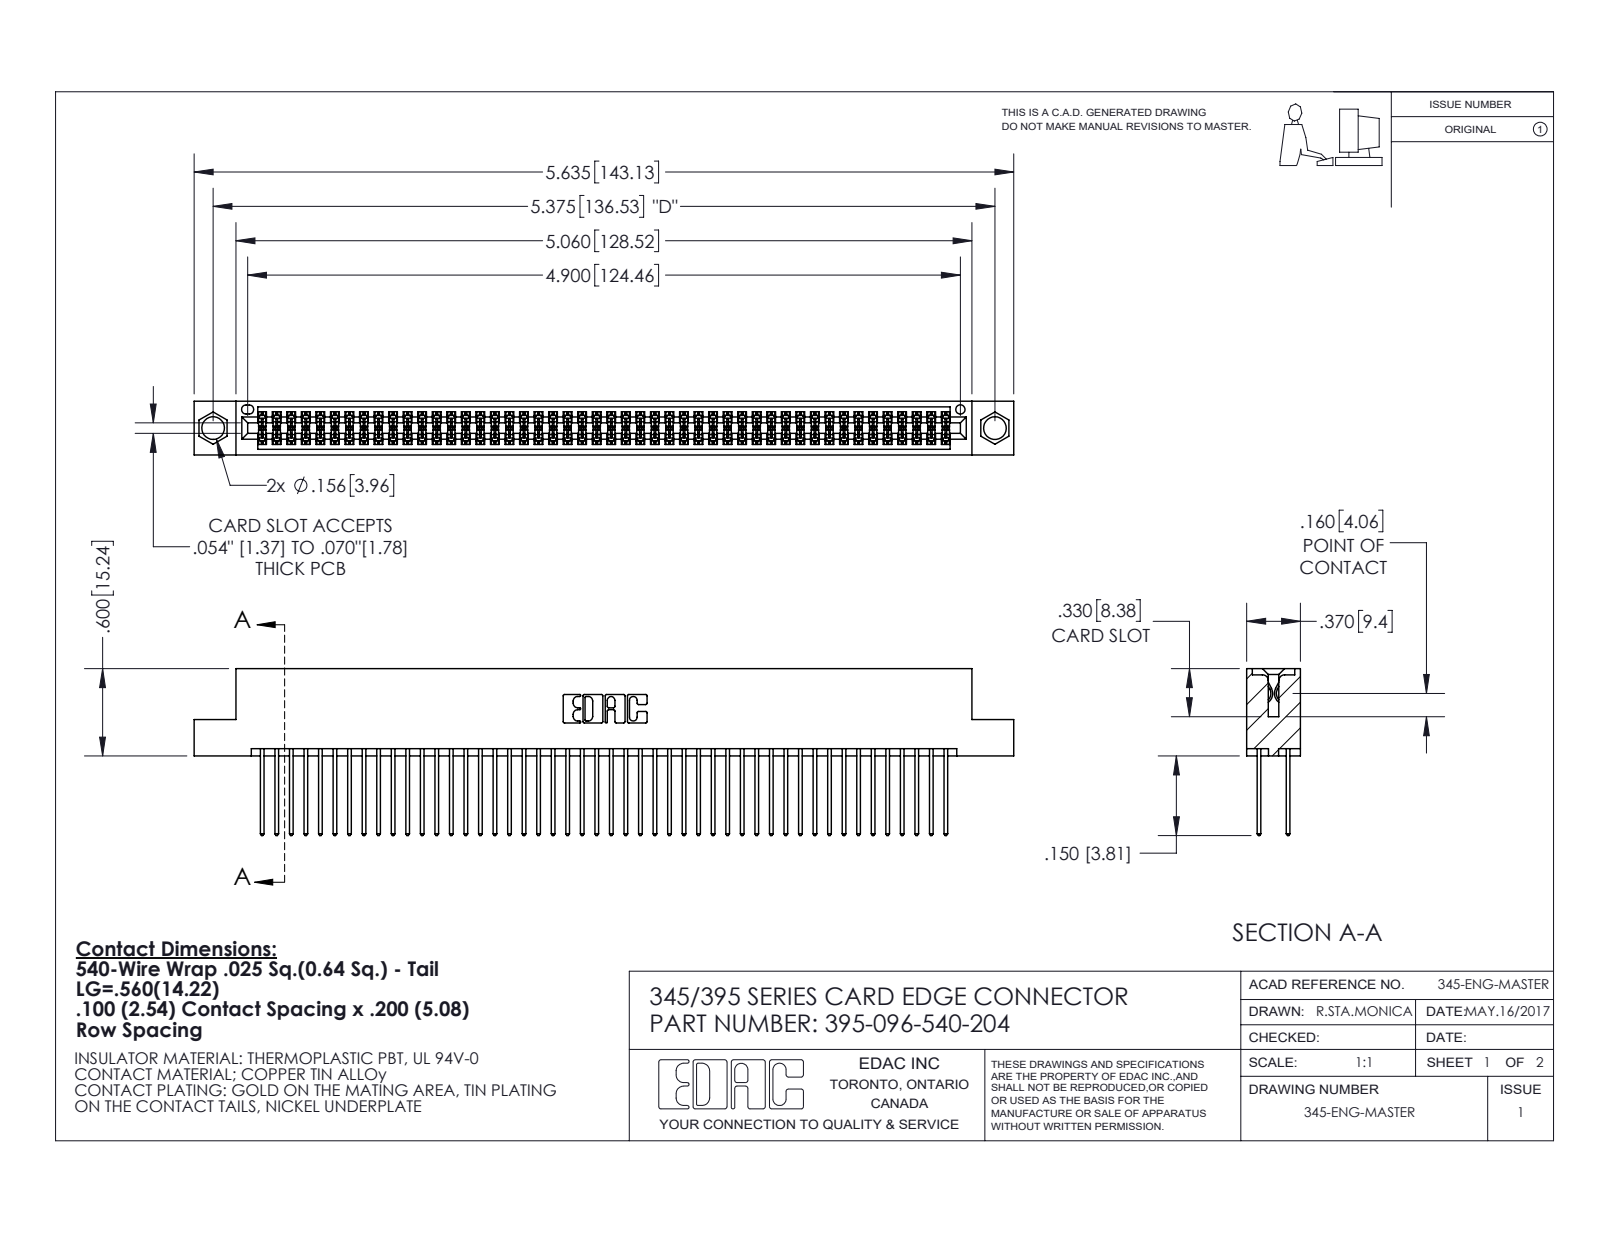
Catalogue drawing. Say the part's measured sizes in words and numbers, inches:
The part is named "345-292-001_345-293-140; 395-096-540-204; 345 Part_Flush Mounting Lugs - 0.156 Dia-TI". Its 3-D file was written by "SolidWorks 2020 (CONFIG_CONTROL_DESIGN)". It is 97 solids with 4940 faces: 3262 planar, 1678 cylindrical and 0 other. Overall it measures 5.635 by 1.147 by 0.37 inches. Its volume is 0.868 cubic inches and its surface area 35.14 square inches. Round holes: 2 of diameter 0.156, 1 of diameter 0.064. Partial cylindrical surfaces (rounded edges, fillets, slot ends): 192 of radius 0.006, 96 of radius 0.01, 22 of radius 0.01, 6 of radius 0.007, 6 of radius 0.031, 3 of radius 0.026, 2 of radius 0.014, 2 of radius 0.019. The main face-to-face distances are 0.072, 0.298, 0.2, 0.098, 0.272, 0.025, 0.37, 0.225, 0.175, 0.149. The hole center spacings are 0.27, 5.139, 5.375.
